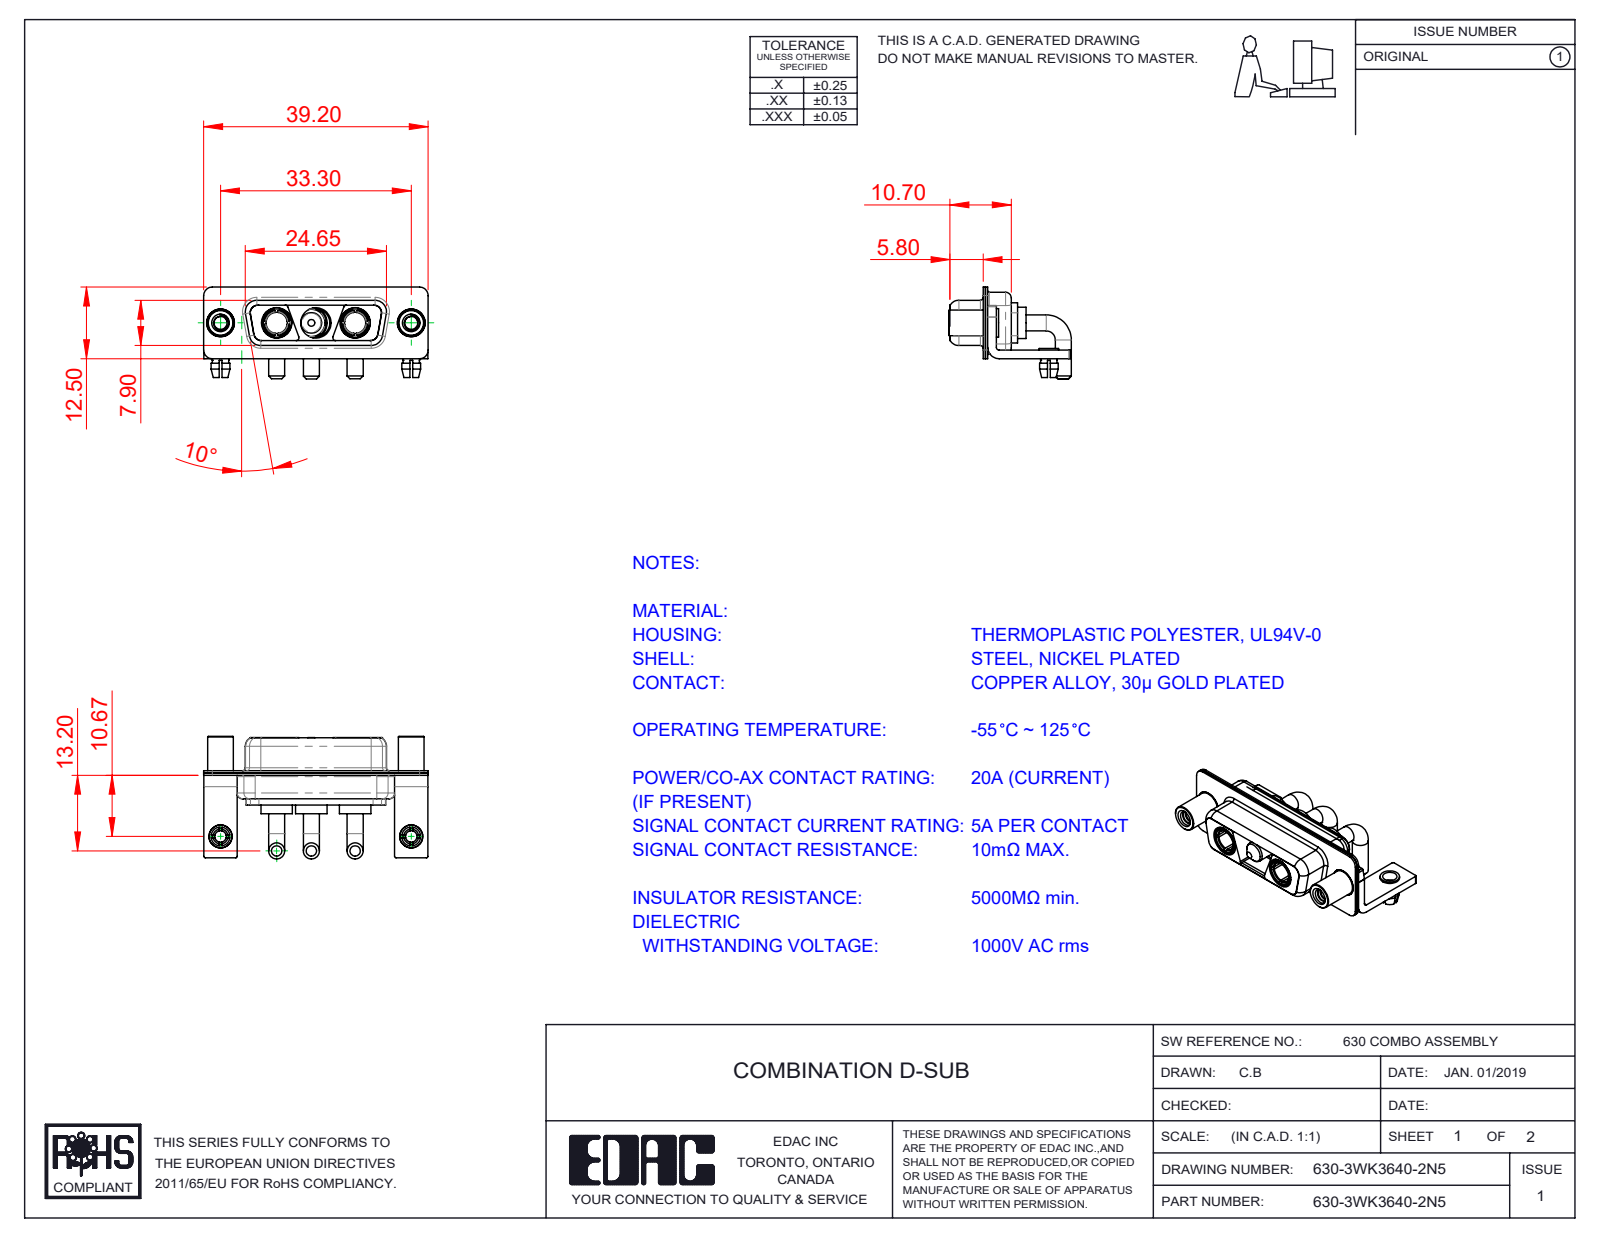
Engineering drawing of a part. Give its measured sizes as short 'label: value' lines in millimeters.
name: Power Pin_20A RA; 630Combo Shell Rear_15 Contacts; Power Socket_20A RA; 630Combo Stabilizer Bracket (+5 more)
written by: SolidWorks 2020 (CONFIG_CONTROL_DESIGN)
unit: mm
bodies: 15 solids, 668 faces (210 planar, 305 cylindrical, 153 other)
size: 39.2 × 21.4 × 16.05
volume: 2 927 mm³; area: 6 816 mm²
holes: 5× ⌀4.85, 3× ⌀5.3, 2× ⌀2, 2× ⌀2.26, 2× ⌀2.5, 2× ⌀3.2, 2× ⌀3.7, 2× ⌀4, 2× ⌀4.05
bosses: 6× ⌀2.8, 3× ⌀5.5, 3× ⌀5.2, 3× ⌀4.75, 3× ⌀3.75, 2× ⌀5, 2× ⌀4.96, 2× ⌀4.95
rounds: 16× R0.25, 16× R1.5, 13× R2, 12× R1.35, 9× R0.5, 8× R1.6, 4× R0.6, 4× R0.65
face distances: 0.4, 0.8, 1.4, 1.5, 0.45, 8.45, 1.8, 8.9, 7.05, 5.2
hole spacings: 6.85, 9.8, 16.65, 23.5, 33.3, 13.7
